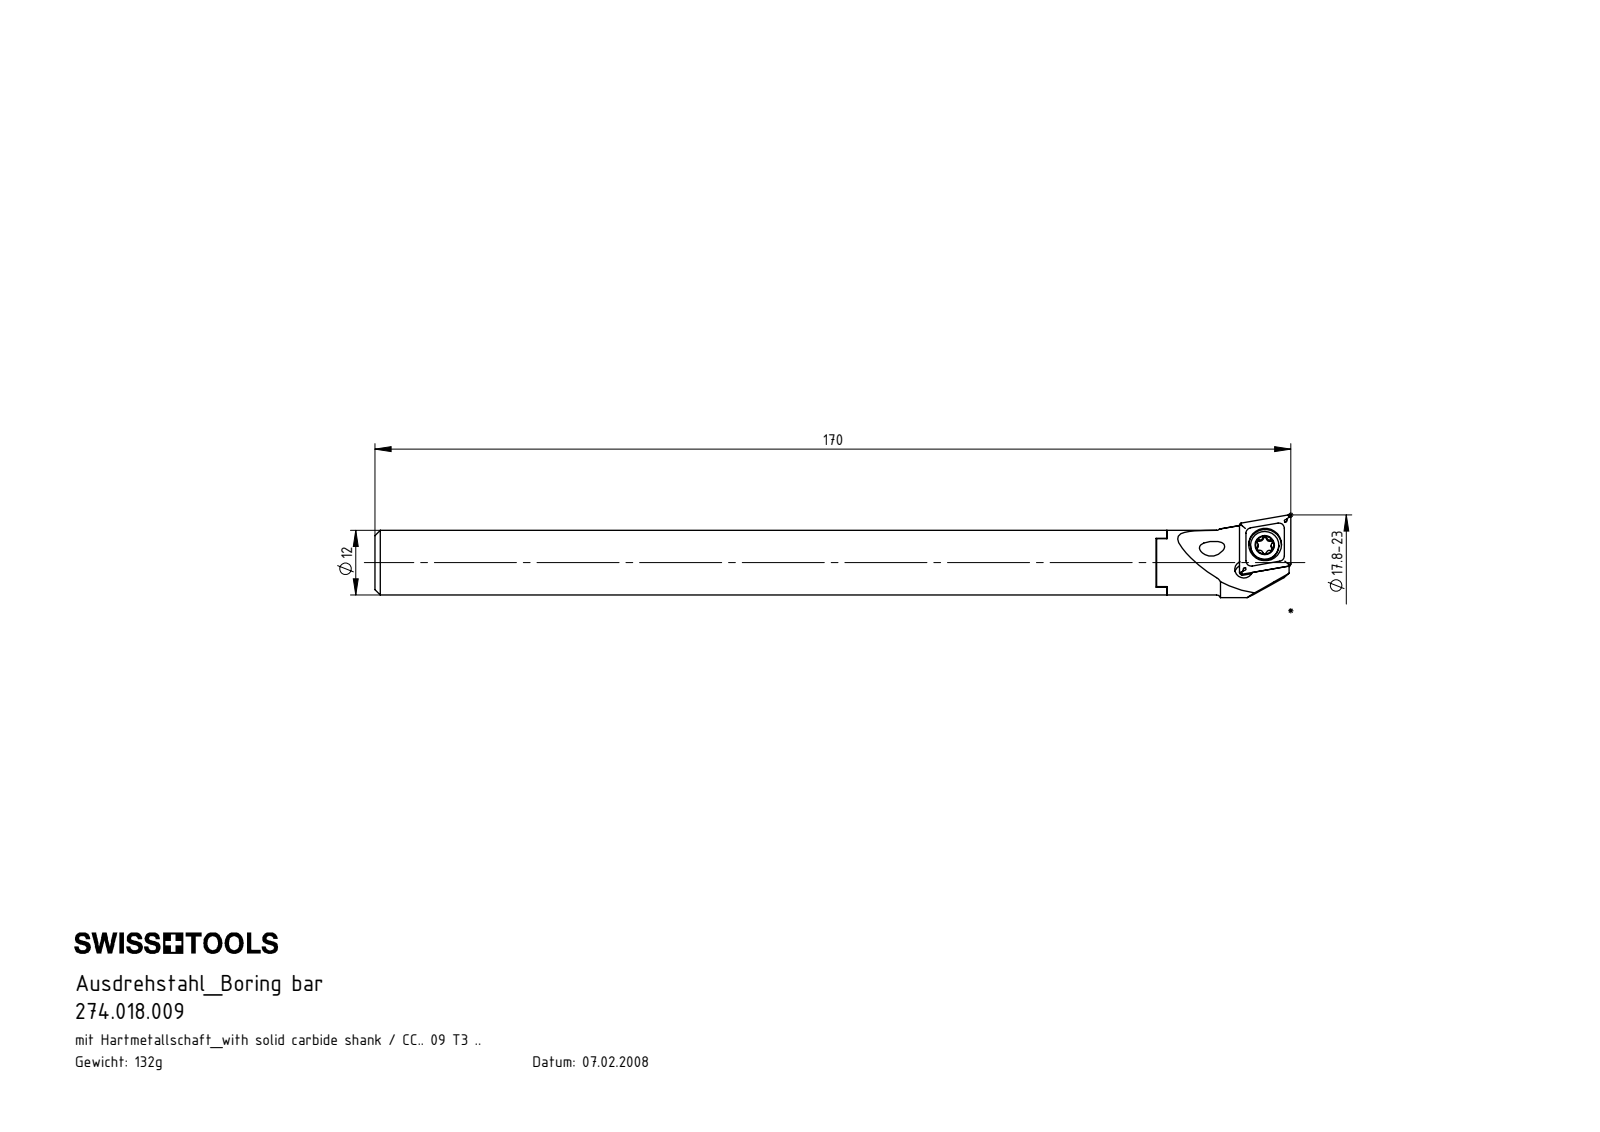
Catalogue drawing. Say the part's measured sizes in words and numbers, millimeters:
The part is named "HM2-BG1.001.025_B; B18-WCB.K13.170_A; WCB-ER2.001.009_A; B18-WCB.K13.170 (+2 more)". Its 3-D file was written by "SolidWorks 2012 (CONFIG_CONTROL_DESIGN)". It is 4 solids with 141 faces: 41 planar, 42 cylindrical and 58 other. Overall it measures 170 by 15.38 by 14.2 millimeters. Its volume is 16 762 cubic millimeters and its surface area 9 280 square millimeters. Round holes: 2 of diameter 3.3, 1 of diameter 3, 1 of diameter 4, 1 of diameter 4.2, 1 of diameter 4.4, 1 of diameter 6.1. Round bosses or shafts: 1 of diameter 12, 1 of diameter 5.25, 1 of diameter 4. Partial cylindrical surfaces (rounded edges, fillets, slot ends): 6 of radius 0.34, 6 of radius 0.59, 1 of radius 6.5, 1 of radius 6.75, 1 of radius 7.5, 1 of radius 10. The main face-to-face distances are 146.95, 147.05, 1.95, 7.95, 4.07, 145, 2.05, 145.1, 1.85, 8.04. The hole center spacings are 6.07, 6.19.
